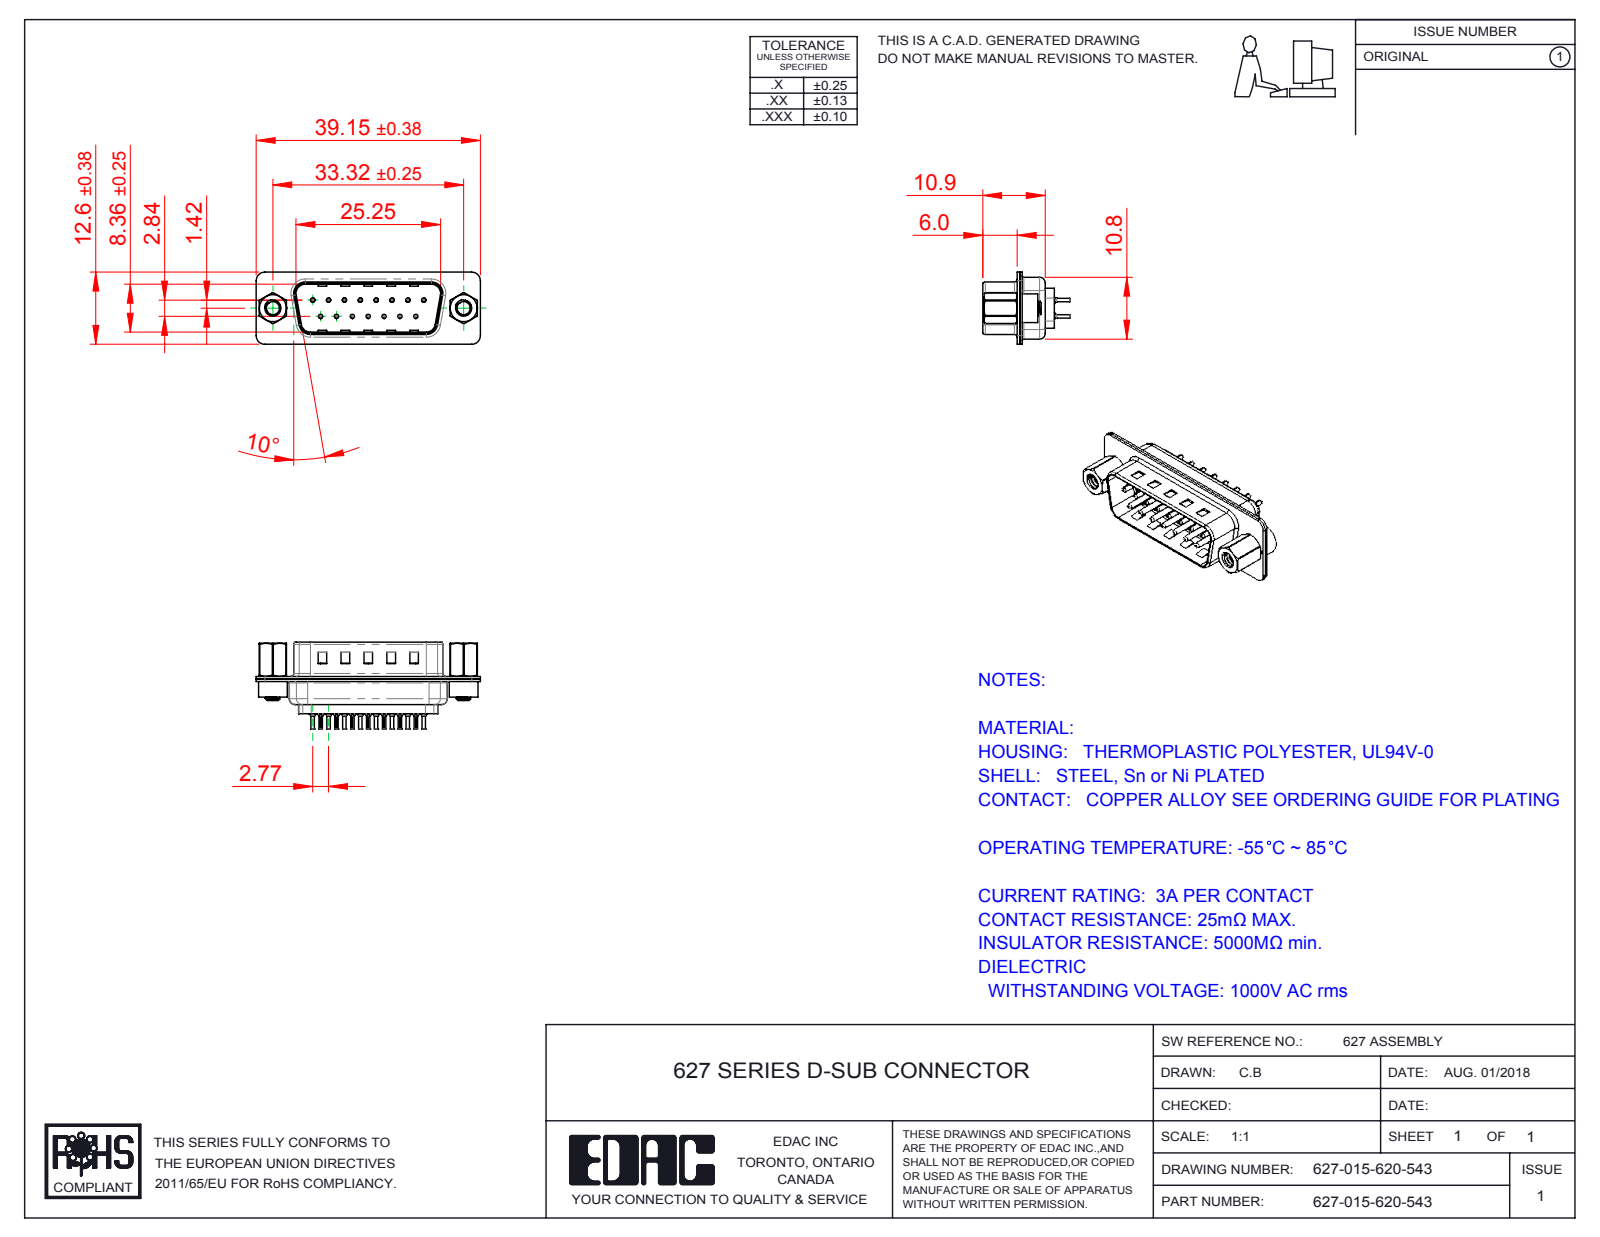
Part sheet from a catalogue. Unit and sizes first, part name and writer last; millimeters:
Units: millimetres
Overall size (bounding box): 39.15 × 15.2 × 12.6
Round holes (diameter × count): ⌀0.2 ×15, ⌀0.35 ×15, ⌀1.1 ×15, ⌀1.6 ×15, ⌀2.26 ×2, ⌀2.29 ×2, ⌀4 ×2, ⌀4.8 ×2
Round bosses / shafts (diameter × count): ⌀2 ×15, ⌀1.5 ×15, ⌀0.75 ×15, ⌀0.6 ×15, ⌀5 ×2, ⌀4.9 ×2, ⌀2.79 ×2
Partial cylindrical surfaces — rounded edges, fillets, slot ends (radius × count): R0.1 ×30, R1.5 ×16, R2 ×12, R0.5 ×8, R1.6 ×8, R0.25 ×4, R0.6 ×4, R0.65 ×4
Main face-to-face distances: 0.4, 0.45, 0.9, 0.82, 9.58, 8.76, 1.5, 1.4, 5.6, 6.5
Hole centre spacings: 3.16, 2.77, 5.54, 8.31, 11.08, 5.03, 5.04, 7.48
Volume: 2 037 mm³ · Surface area: 5 791 mm²
Bodies: 22 solids, 1936 faces (521 planar, 760 cylindrical, 655 other)
Part name (STEP PRODUCT): 627 Contact Row 1_20L; 627 Shell Front_15 Contacts; 627 Shell Rear_15 Contacts; 627 Contact Row 2_20L (+4 more)
STEP written by: SolidWorks 2016 (CONFIG_CONTROL_DESIGN)
